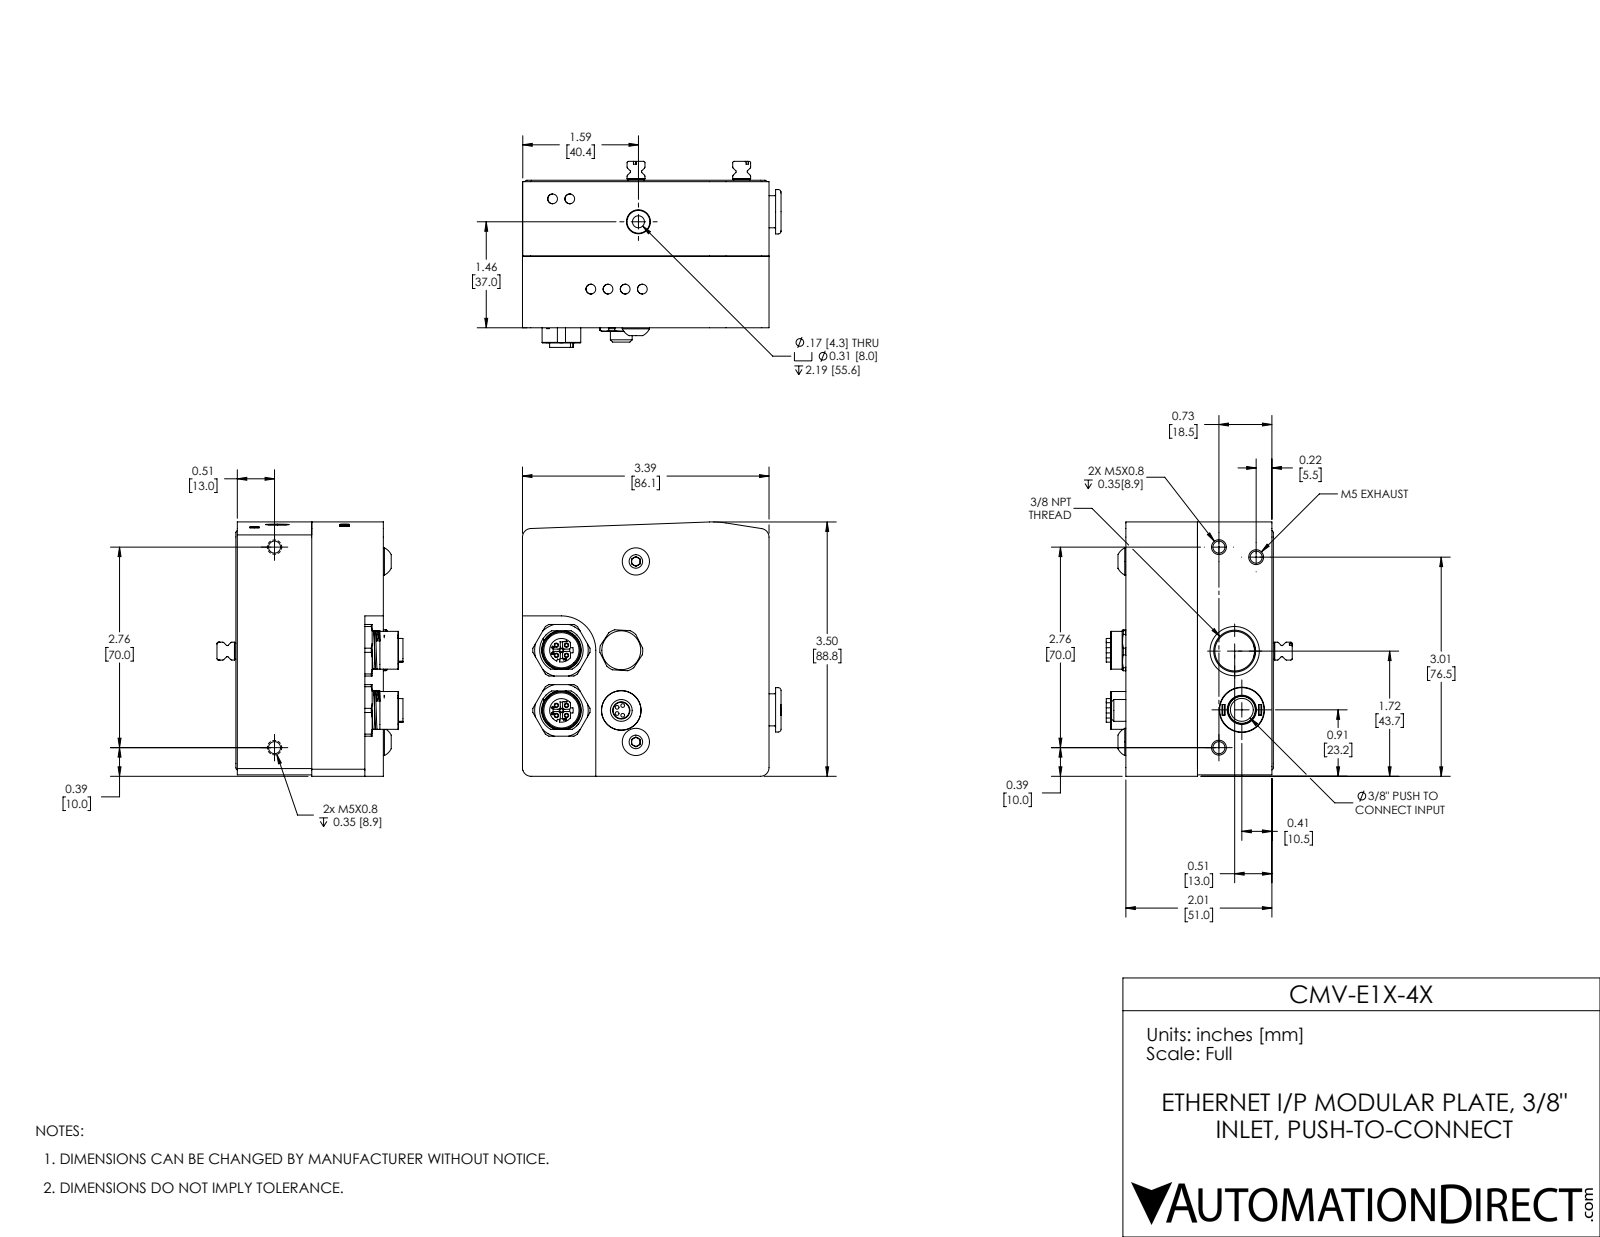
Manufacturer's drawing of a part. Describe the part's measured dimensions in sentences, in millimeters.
The part is named "CMV-E1X-4X". Its 3-D file was written by "SolidWorks 2017 (AUTOMOTIVE_DESIGN)". It is 18 solids with 1676 faces: 720 planar, 507 cylindrical and 449 other. Overall it measures 90.3 by 88.8 by 64.95 millimeters. Its volume is 364 743 cubic millimeters and its surface area 63 971 square millimeters. Round holes: 10 of diameter 1.1, 7 of diameter 4.2, 6 of diameter 3.4, 2 of diameter 5.5, 2 of diameter 8, 2 of diameter 8.8, 2 of diameter 11, 2 of diameter 11.9, 2 of diameter 12.32, 2 of diameter 13.8, 2 of diameter 16.6, 1 of diameter 1. Round bosses or shafts: 4 of diameter 1.5, 4 of diameter 1.3, 4 of diameter 0.98, 4 of diameter 0.5, 2 of diameter 13.5, 2 of diameter 9.5, 2 of diameter 8.25, 2 of diameter 6.25. Partial cylindrical surfaces (rounded edges, fillets, slot ends): 60 of radius 0.1, 40 of radius 0.85, 24 of radius 0.2, 8 of radius 0.8, 8 of radius 3, 4 of radius 0.6, 4 of radius 2.3, 2 of radius 0.5. The main face-to-face distances are 26, 25, 51, 86, 0.5, 86.1, 1, 44.55, 18.55, 6.45. The hole center spacings are 2.5, 3.54, 21, 5.01, 19.21, 19.31, 21.3, 22.74.
